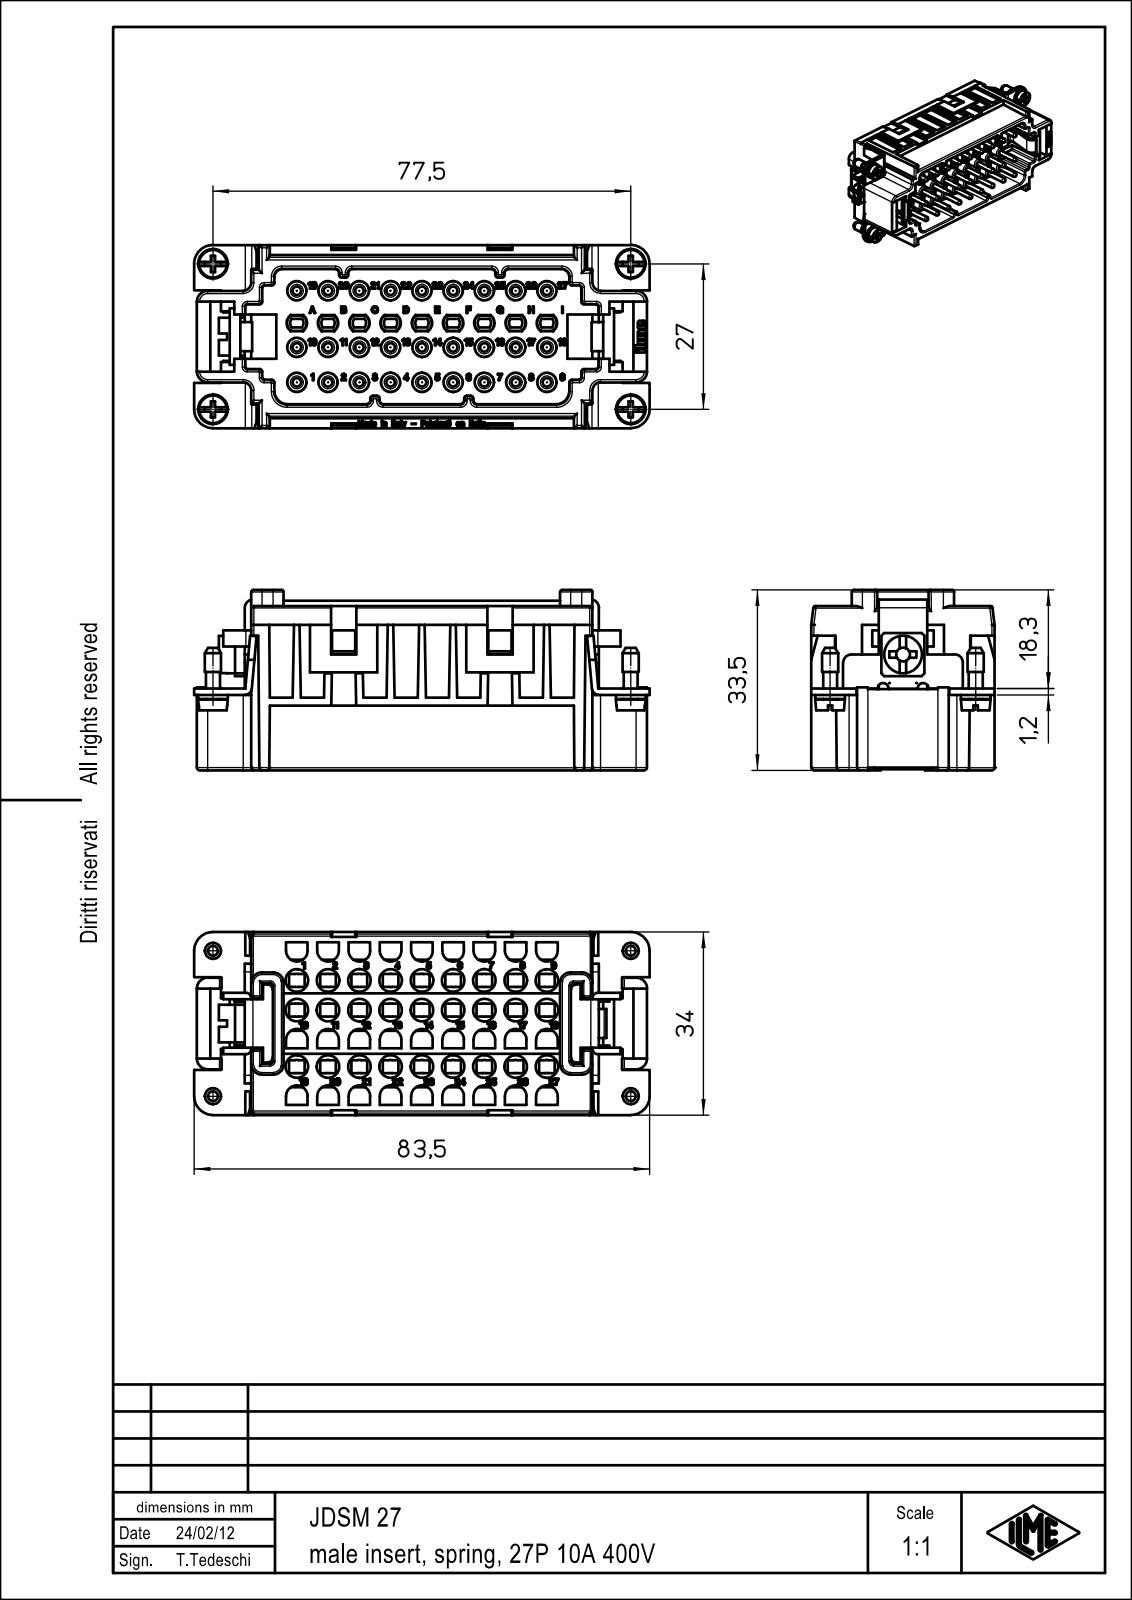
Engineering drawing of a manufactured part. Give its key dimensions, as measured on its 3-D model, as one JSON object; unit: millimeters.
{"part_name": "JDSM_27", "step_written_by": "Creo Elements/Direct Modeling 18.0B 02-Dec-2011 (C) Parametric Technology GmbH (AUTOMOTIVE_DESIGN)", "units": "millimeters", "bodies": {"solids": 1, "faces": 6617, "planar": 5843, "cylindrical": 422, "other": 352}, "overall_size": [84.5, 34, 33.5], "volume_mm3": 46701, "surface_area_mm2": 24112, "round_holes": [[4.2, 27], [2.58, 1], [3, 1]], "round_bosses_or_shafts": [[1.6, 27], [5.5, 4], [3, 4], [2.6, 4], [7, 1]], "partial_cylinders_radius": [[0.5, 60], [2, 41], [0.4, 19], [1, 14], [1.5, 10], [1.25, 9], [1.9, 9], [0.8, 8]], "face_to_face_distances": [0.9, 2, 13, 1.2, 33.1, 18.5, 1, 8.5, 7.6, 15], "hole_center_spacings": [5.8, 11.6, 17.4, 7.99, 12, 17.02, 23.2, 12.84]}
